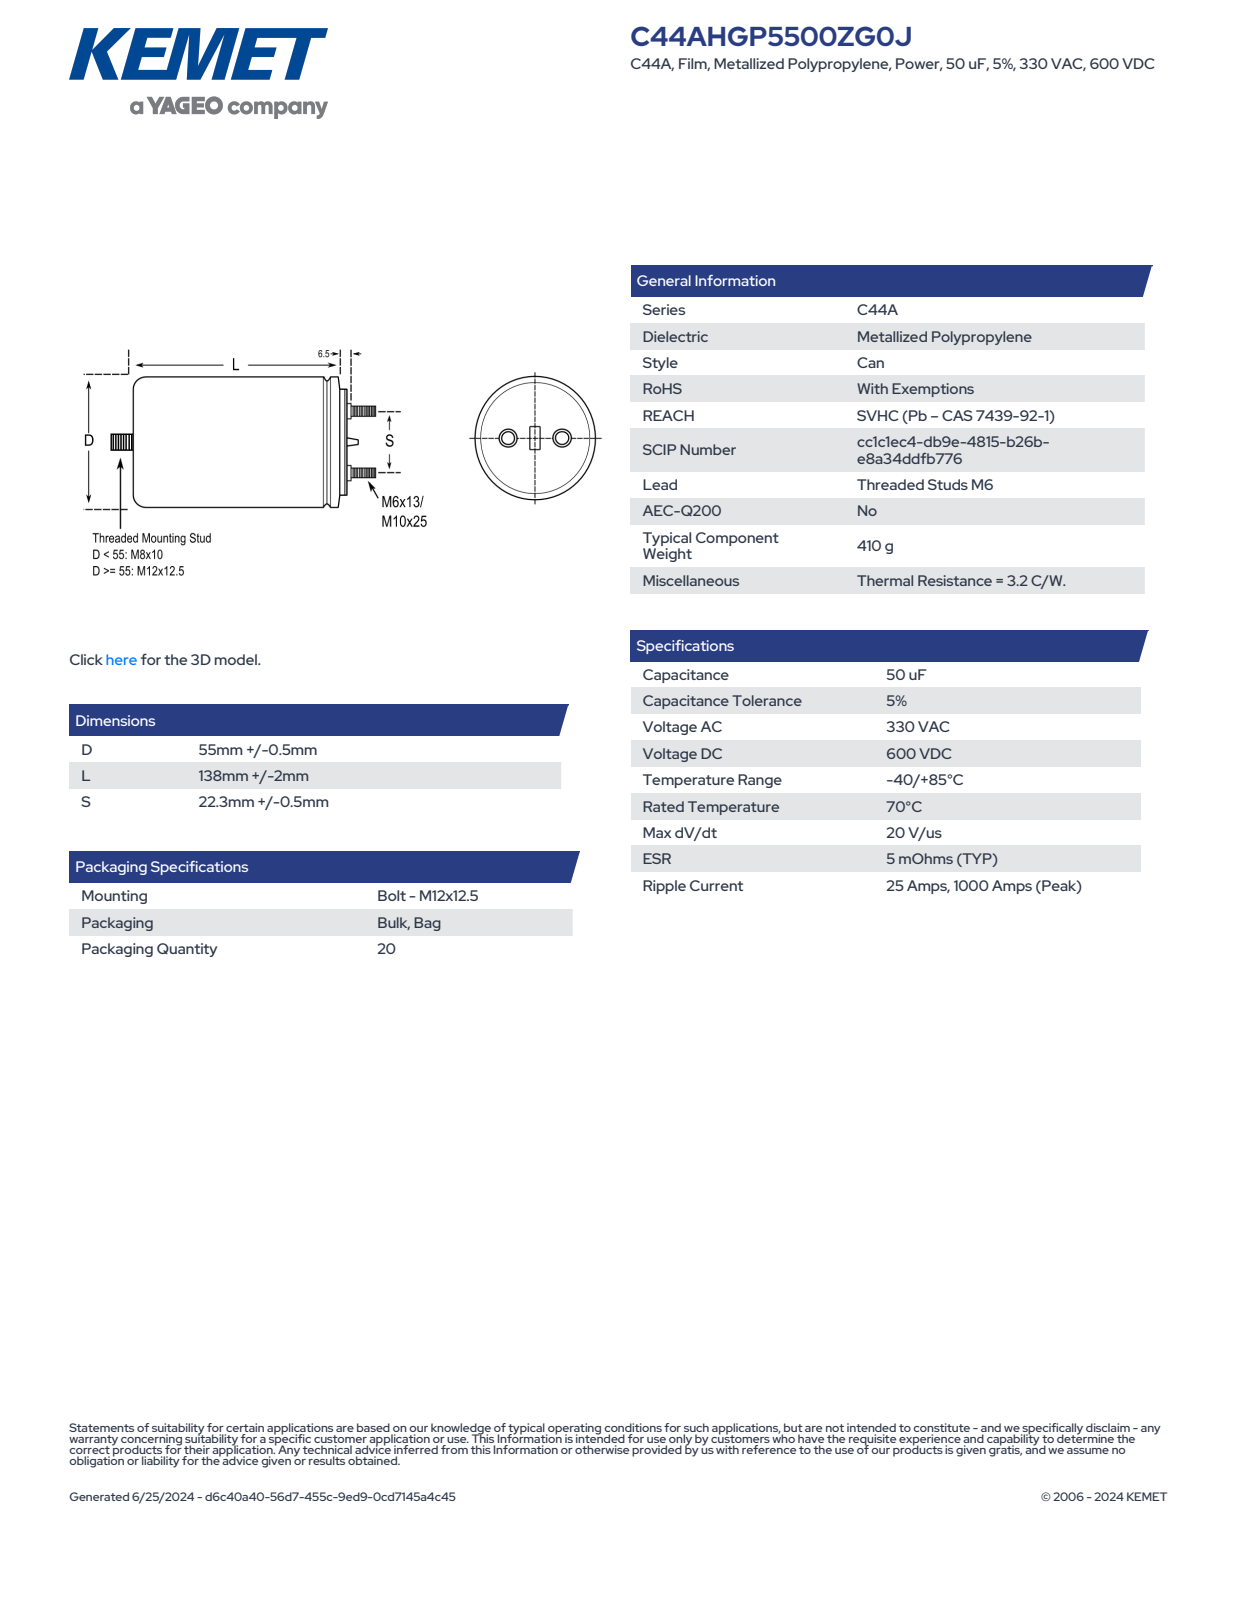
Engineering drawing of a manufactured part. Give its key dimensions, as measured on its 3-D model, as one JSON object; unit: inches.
{"part_name": "CFP_C44A_55X138_D55.5L140S22.3", "step_written_by": "SolidWorks 2014 (AUTOMOTIVE_DESIGN)", "units": "inches", "bodies": {"solids": 1, "faces": 102, "planar": 29, "cylindrical": 34, "other": 39}, "overall_size": [6.772, 2.185, 2.185], "volume_in3": 21.09, "surface_area_in2": 47.34, "round_bosses_or_shafts": [[0.354, 2], [0.236, 2], [2.185, 1], [1.714, 1], [0.472, 1]], "partial_cylinders_radius": [[1.092, 1]], "face_to_face_distances": [5.709, 0.492, 6.201, 6.26, 5.768, 0.059, 6.772, 6.28, 0.571, 0.512]}
